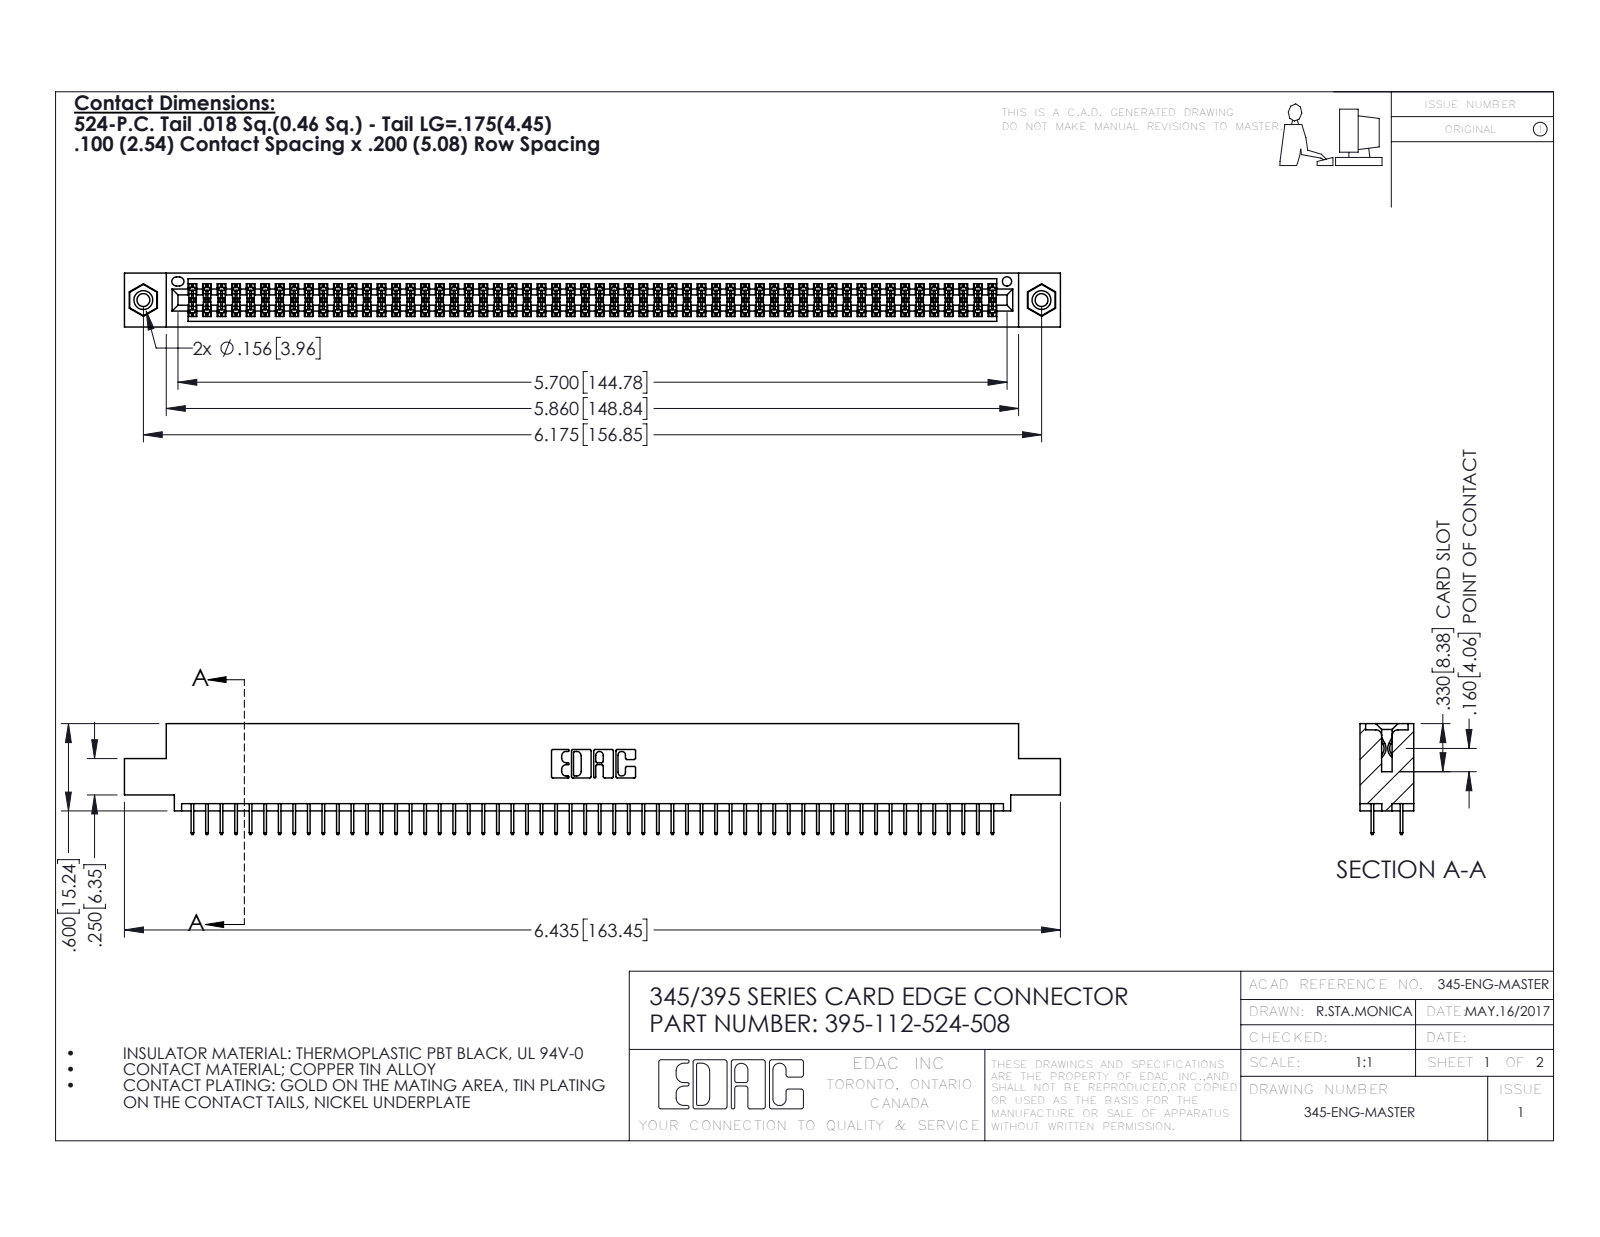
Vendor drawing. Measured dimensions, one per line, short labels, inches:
name: 345-250-001_345-250-003-102; 345 Part_0.110 Offset - 0.156 Dia-TI; 345-292-001_345-293-124; 395-112-524-508
written by: SolidWorks 2016 (CONFIG_CONTROL_DESIGN)
unit: in
bodies: 115 solids, 6238 faces (4484 planar, 1738 cylindrical, 16 other)
size: 6.435 × 0.762 × 0.37
volume: 0.962 in³; area: 36 in²
holes: 2× ⌀0.089, 2× ⌀0.125, 2× ⌀0.156, 1× ⌀0.064
bosses: 2× ⌀0.155
rounds: 168× R0.006, 22× R0.01, 6× R0.007, 6× R0.031, 3× R0.026, 2× R0.014, 2× R0.019, 2× R0.022
face distances: 0.072, 0.298, 0.2, 0.37, 0.098, 0.272, 0.025, 0.225, 0.072, 0.175
hole spacings: 0.27, 5.939, 6.175
